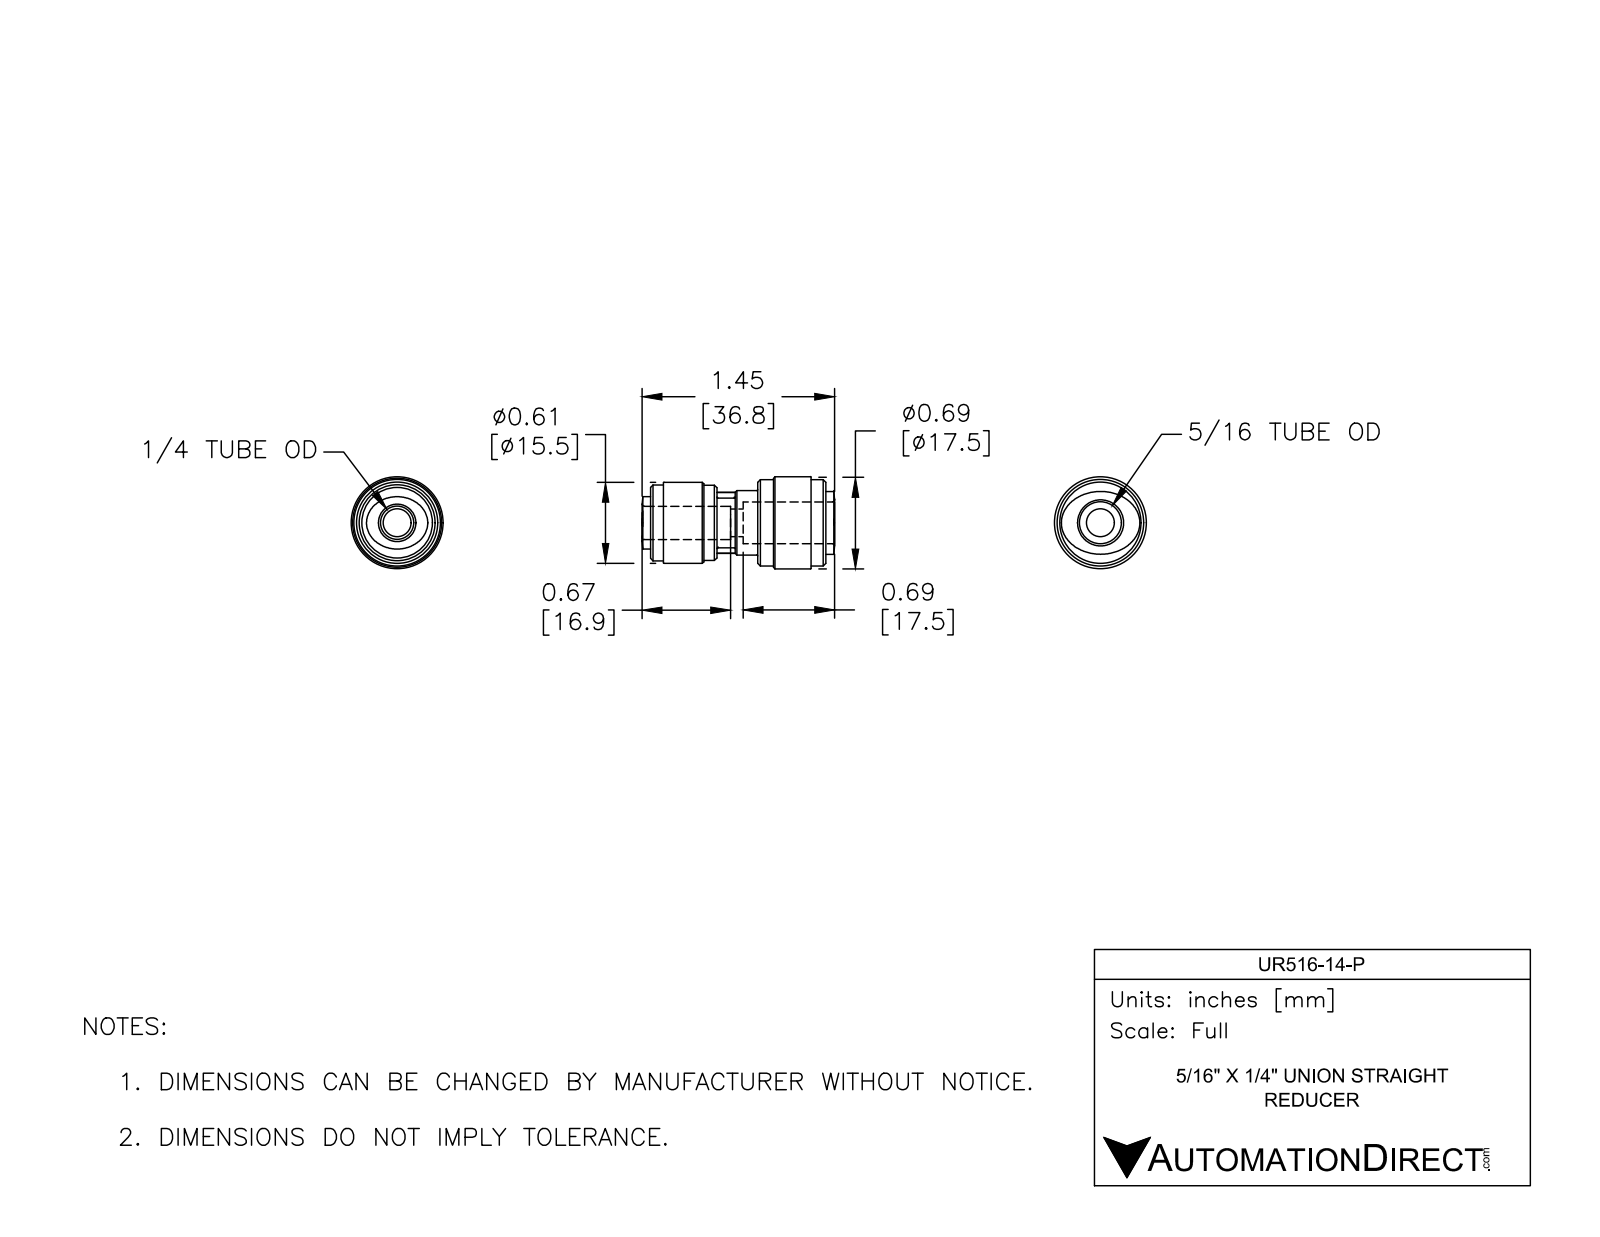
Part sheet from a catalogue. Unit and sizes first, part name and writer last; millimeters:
Units: millimetres
Overall size (bounding box): 36.8 × 17.6 × 17.6
Round holes (diameter × count): ⌀5.3 ×1, ⌀6.4 ×1, ⌀8 ×1
Round bosses / shafts (diameter × count): ⌀17.6 ×1, ⌀16.5 ×1, ⌀15.5 ×1, ⌀14.5 ×1, ⌀14.4 ×1, ⌀12.3 ×1, ⌀9.6 ×1
Partial cylindrical surfaces — rounded edges, fillets, slot ends (radius × count): R5.8 ×1
Main face-to-face distances: 13, 20.5, 7.8, 10.2, 2.8, 12.7, 33.5, 20.8, 18, 2.5
Volume: 4 920 mm³ · Surface area: 3 086 mm²
Bodies: 1 solid, 79 faces (16 planar, 25 cylindrical, 38 other)
Part name (STEP PRODUCT): UR516-14-P
STEP written by: SolidWorks 2017 (AUTOMOTIVE_DESIGN)
